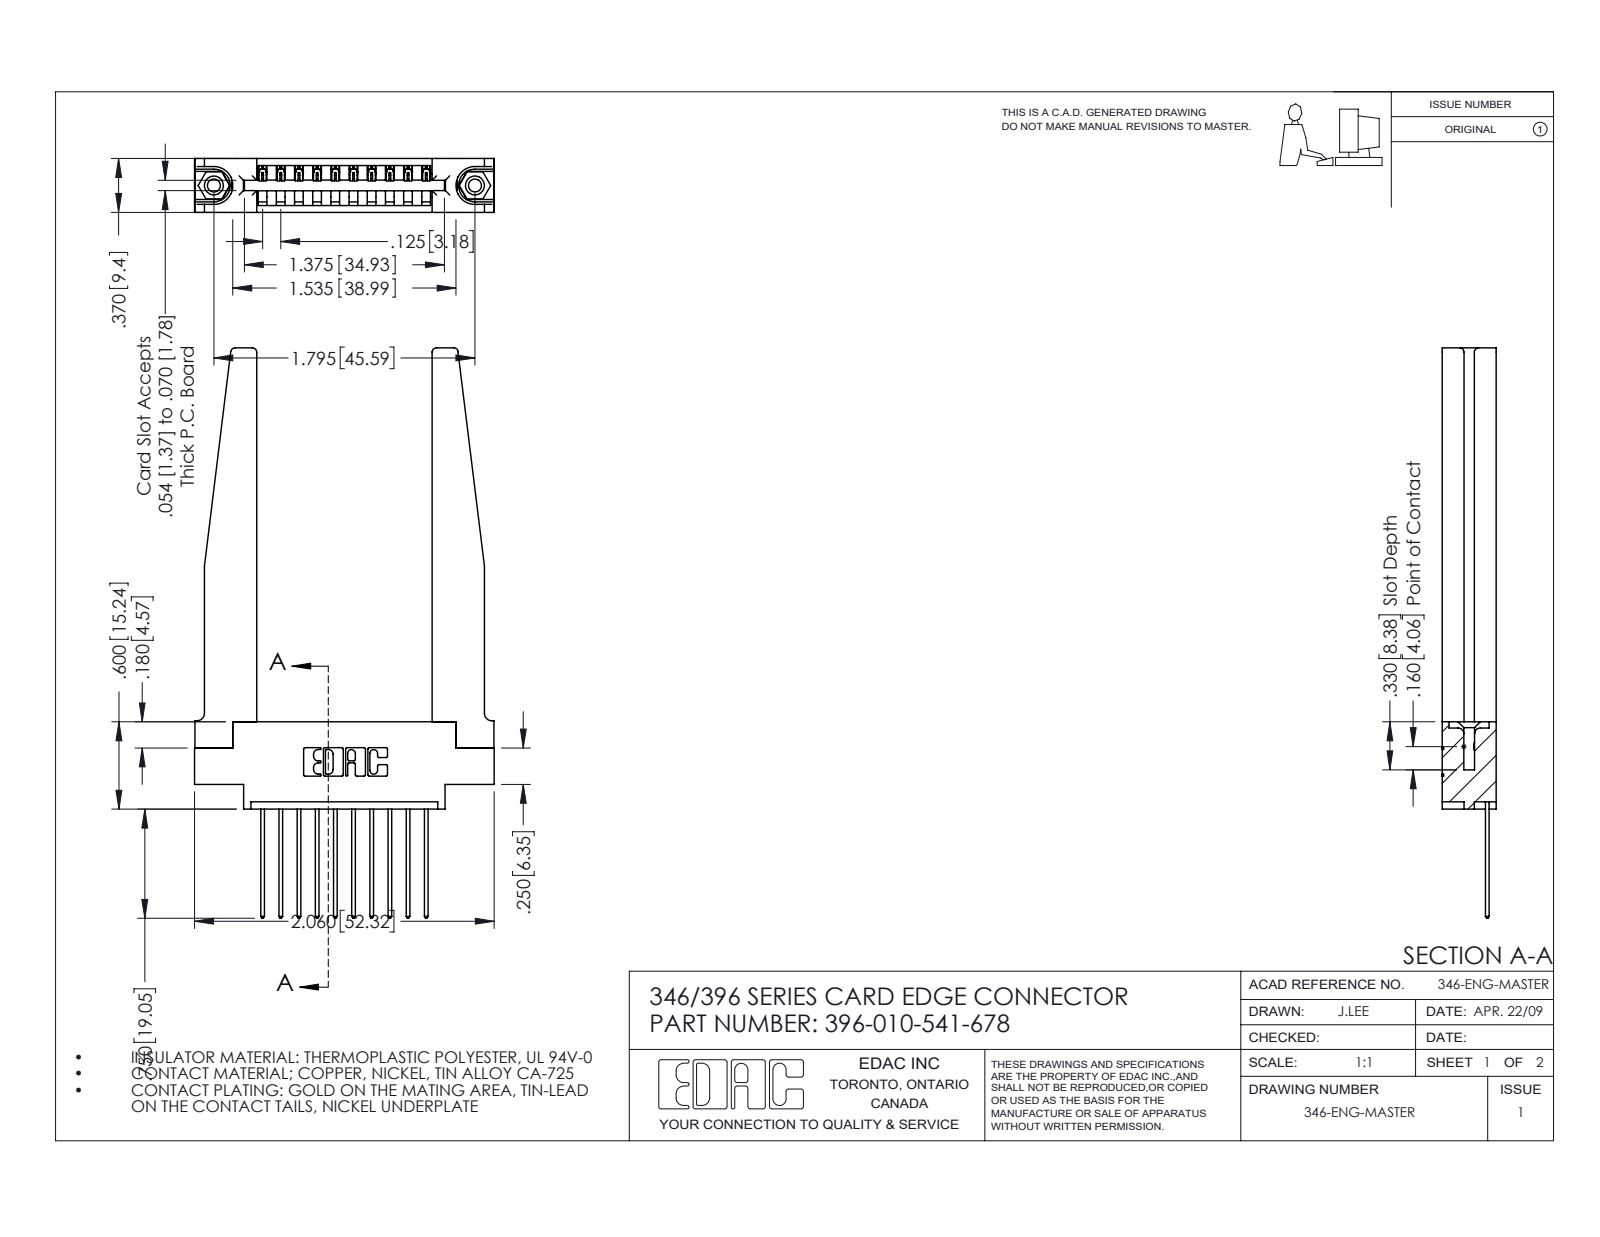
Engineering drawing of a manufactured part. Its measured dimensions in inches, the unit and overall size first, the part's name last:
Units: inches
Overall size (bounding box): 3.92 × 2.06 × 0.37
Round holes (diameter × count): ⌀0.089 ×2, ⌀0.125 ×2, ⌀0.156 ×2, ⌀0.064 ×1
Round bosses / shafts (diameter × count): ⌀0.155 ×2
Partial cylindrical surfaces — rounded edges, fillets, slot ends (radius × count): R0.01 ×22, R0.006 ×20, R0.01 ×20, R0.03 ×8, R0.007 ×6, R0.031 ×6, R0.026 ×3, R0.031 ×2
Main face-to-face distances: 0.37, 0.15, 0.072, 0.148, 0.048, 0.322, 0.25, 0.22, 0.102, 0.173
Hole centre spacings: 0.246, 1.59, 1.795
Volume: 0.706 in³ · Surface area: 19.2 in²
Bodies: 15 solids, 940 faces (622 planar, 266 cylindrical, 52 other)
Part name (STEP PRODUCT): 345-292-001_345-293-141; 345-250-001_345-250-001-102; 346-220-078_345-220-078; 396-010-541-678 (+1 more)
STEP written by: SolidWorks 2016 (CONFIG_CONTROL_DESIGN)
